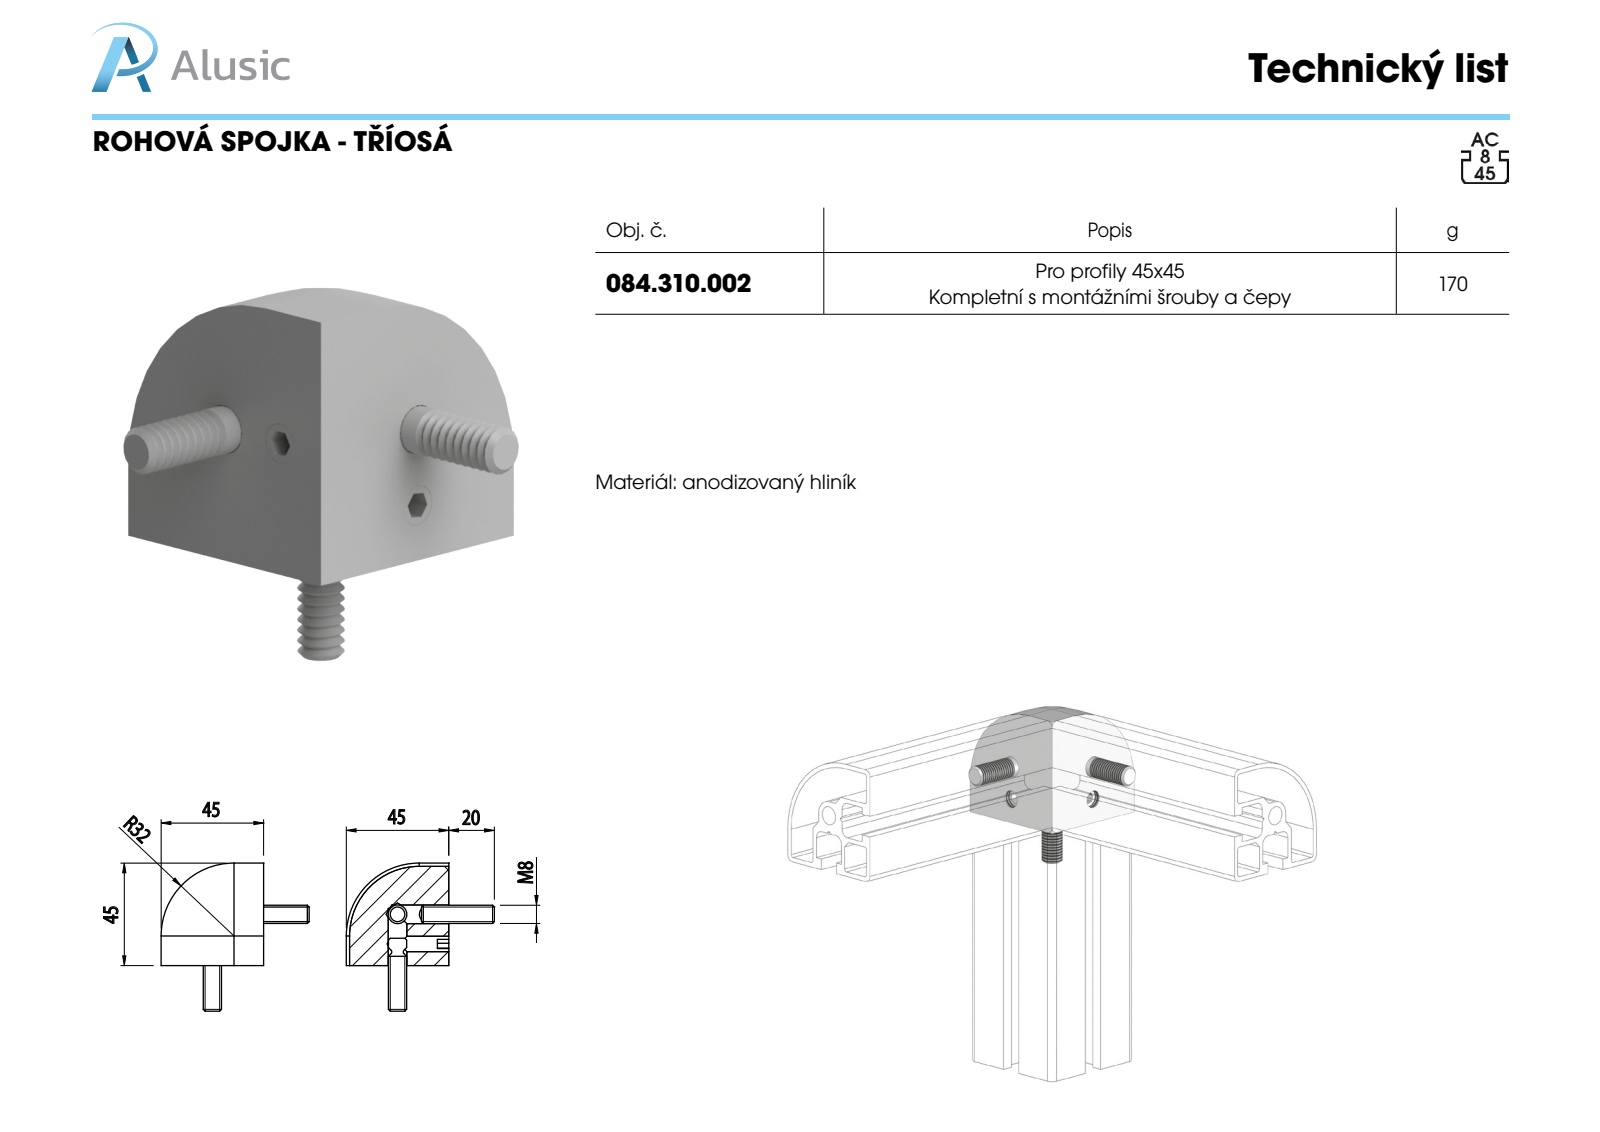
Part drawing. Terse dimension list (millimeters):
name: 084.310.002; socket set screw cone point_iso_ISO 4027 - M8 x 20-C; 203208; 354545
written by: SolidWorks 2011 (CONFIG_CONTROL_DESIGN)
unit: mm
bodies: 6 solids, 152 faces (28 planar, 51 cylindrical, 73 other)
size: 65 × 65 × 65
volume: 67 870 mm³; area: 15 576 mm²
holes: 3× ⌀6.8, 3× ⌀8.2
bosses: 5× ⌀8
rounds: 3× R32
face distances: 45, 33, 12, 65, 32, 20, 4, 40, 7, 5
hole spacings: 13
